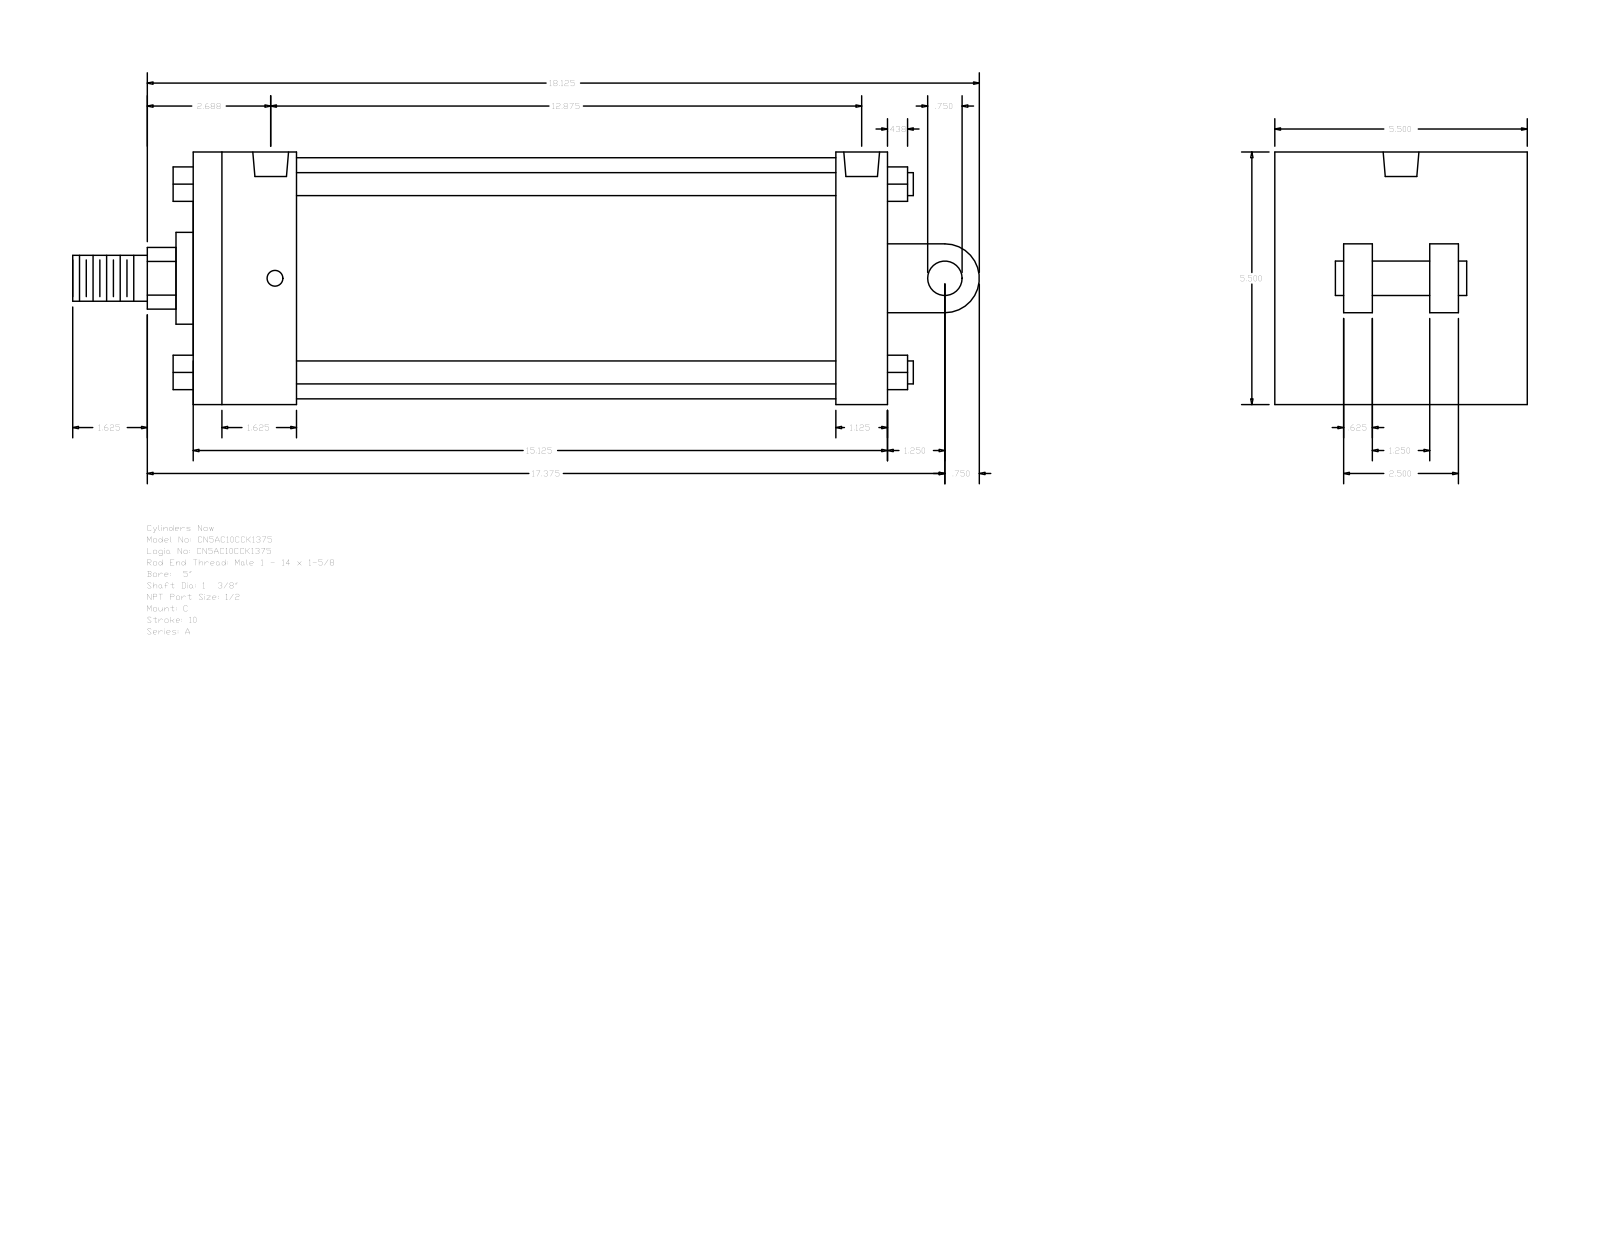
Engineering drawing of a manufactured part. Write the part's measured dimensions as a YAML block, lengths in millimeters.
part_name: "A_C__0500_1.375"
step_written_by: "GSSL Pune (CONFIG_CONTROL_DESIGN)"
units: millimeters
bodies: {solids: 0, faces: 135, planar: 102, cylindrical: 33, other: 0}
overall_size: [501.65, 139.7, 139.7]
round_holes:
  - {diameter: 8.73, count: 4}
  - {diameter: 19.77, count: 2}
round_bosses_or_shafts:
  - {diameter: 12.7, count: 4}
  - {diameter: 133.35, count: 1}
  - {diameter: 50.8, count: 1}
  - {diameter: 34.92, count: 1}
  - {diameter: 25.4, count: 1}
  - {diameter: 19.05, count: 1}
partial_cylinders:
  - {radius: 17.06, count: 1}
  - {radius: 19.05, count: 1}
face_to_face_distances: [139.7, 384.17, 57.15, 355.6, 298.45, 327.02, 28.57, 38.1, 53.97, 101.6]
hole_center_spacings: [2.39, 322.25, 324.64, 327.03]
